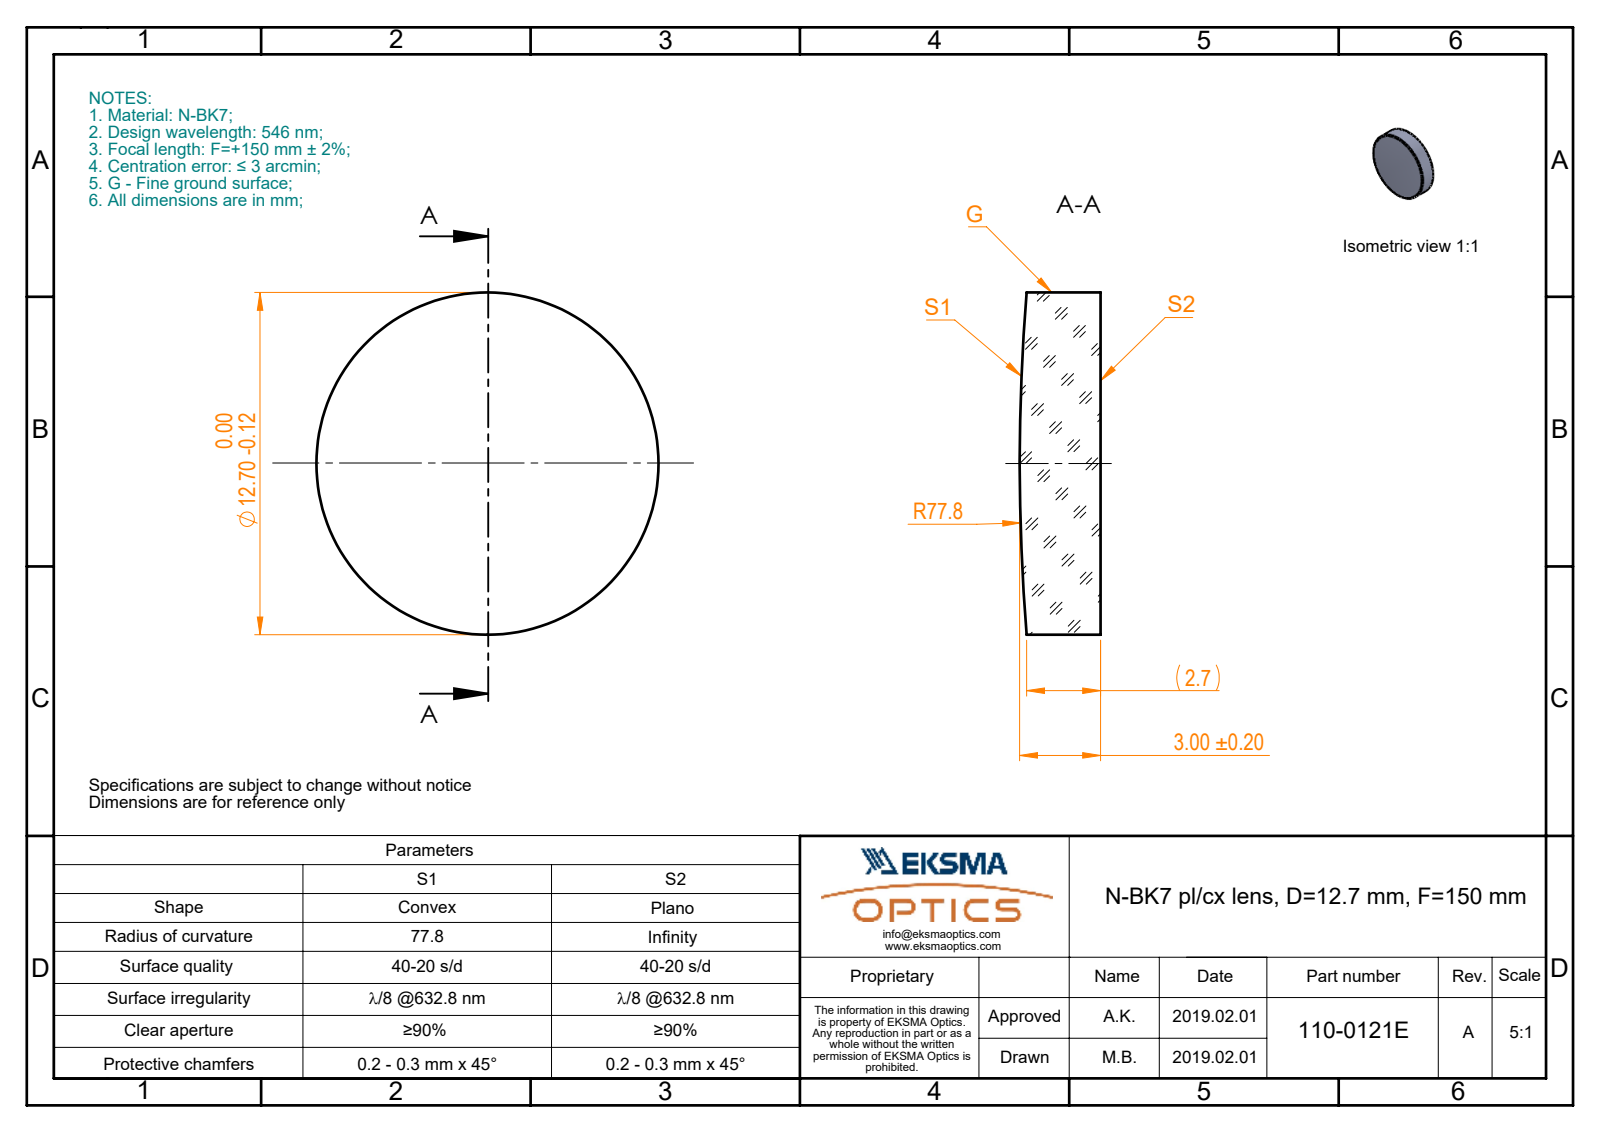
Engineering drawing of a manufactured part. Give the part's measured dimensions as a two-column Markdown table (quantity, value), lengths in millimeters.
| quantity | value |
| --- | --- |
| part name | 110-0121E BK7 pl-cx 12.7 F150 |
| STEP written by | SolidWorks 2017 (CONFIG_CONTROL_DESIGN) |
| units | millimeters |
| bodies | 1 solid, 5 faces (1 planar, 2 cylindrical, 2 other) |
| overall size | 12.7 × 12.7 × 3 |
| volume | 364 mm³ |
| surface area | 363 mm² |
| round bosses / shafts (diameter × count) | 12.7 × 1 |
